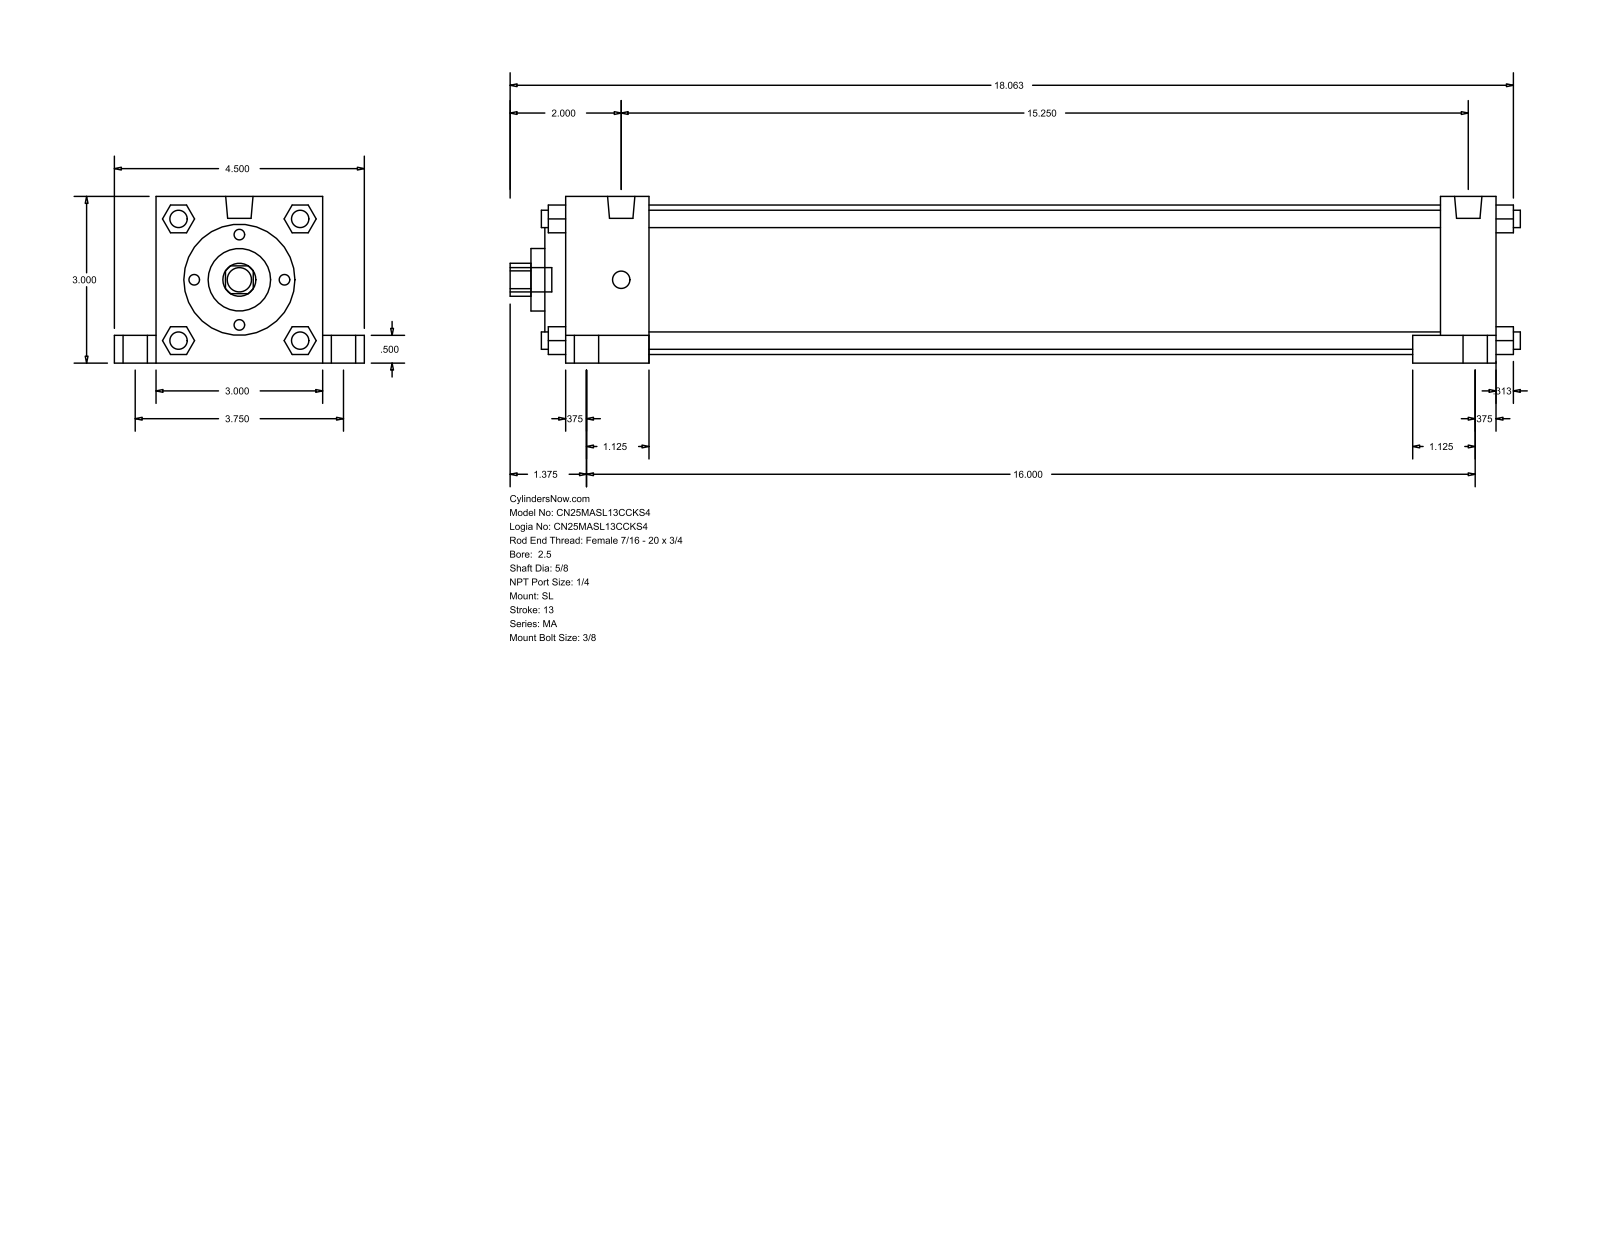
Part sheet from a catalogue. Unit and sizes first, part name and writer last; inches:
Units: inches
Overall size (bounding box): 18.187 × 4.5 × 3
Round holes (diameter × count): ⌀0.625 ×1, ⌀1.125 ×1, ⌀2 ×1, ⌀2.69 ×1
Round bosses / shafts (diameter × count): ⌀0.313 ×8, ⌀0.437 ×5, ⌀0.687 ×4, ⌀0.492 ×2
Partial cylindrical surfaces — rounded edges, fillets, slot ends (radius × count): R0.297 ×1
Main face-to-face distances: 3, 16.75, 0.5, 14.25, 1, 1.5, 15.25, 15.75, 0.75, 2.5
Bodies: 0 solids, 150 faces (113 planar, 37 cylindrical, 0 other)
Part name (STEP PRODUCT): MA_SL__0250_0.625
STEP written by: GSSL Pune (CONFIG_CONTROL_DESIGN)
